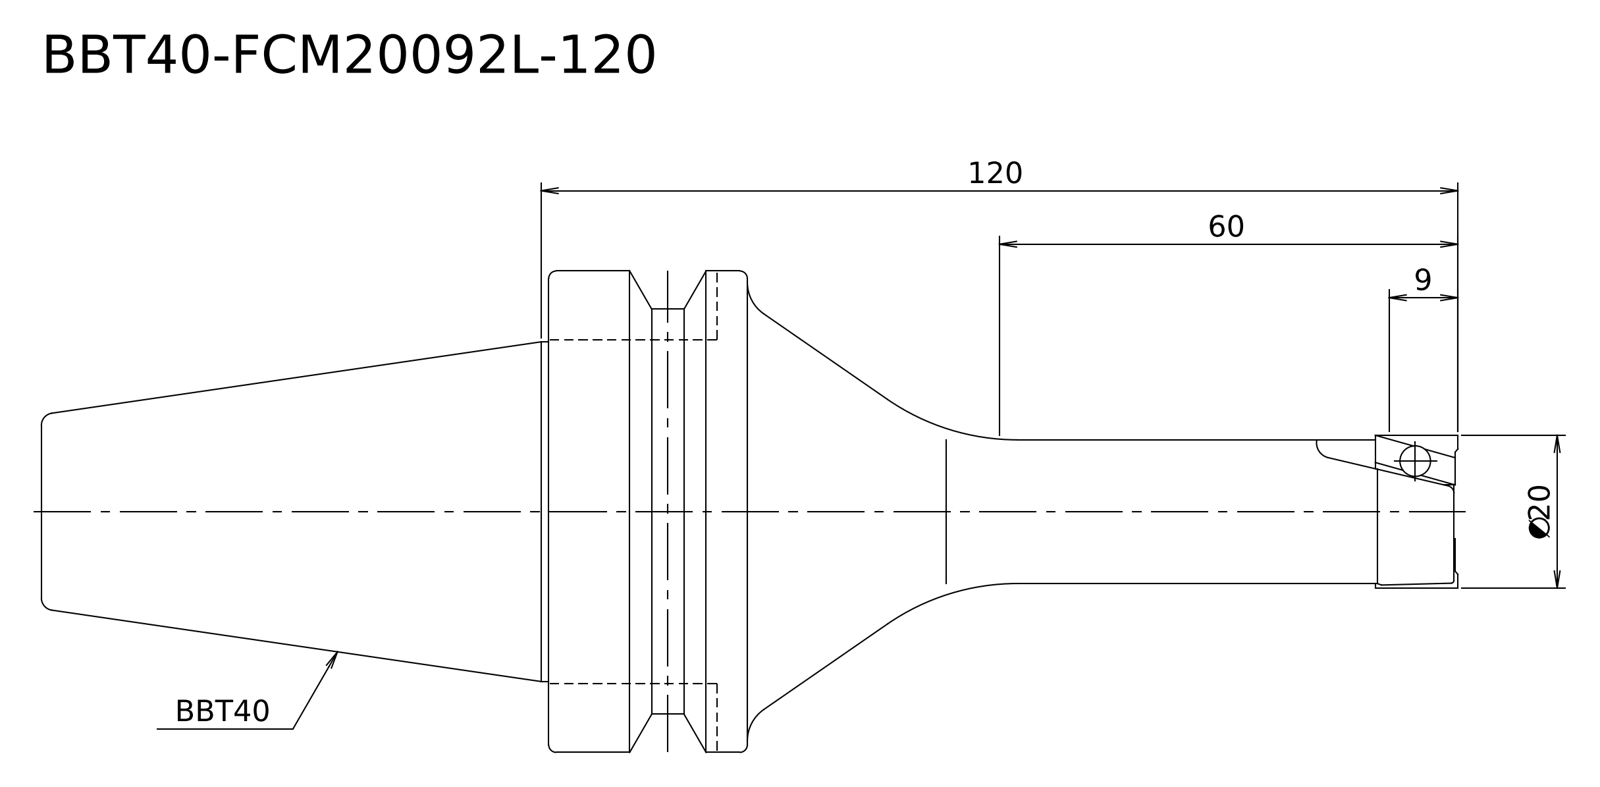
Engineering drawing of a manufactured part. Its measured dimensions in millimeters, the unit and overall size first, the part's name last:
Units: millimetres
Overall size (bounding box): 185.4 × 63 × 63
Round bosses / shafts (diameter × count): ⌀63 ×1, ⌀53 ×1, ⌀44.45 ×1, ⌀20 ×1, ⌀18.8 ×1
Main face-to-face distances: 66.4, 119, 185.4, 93, 26, 92.4
Volume: 191 230 mm³ · Surface area: 24 160 mm²
Bodies: 1 solid, 17 faces (4 planar, 6 cylindrical, 7 other)
STEP written by: Kubotek KeyCreator V8.5.1 (14335) (CONFIG_CONTROL_DESIGN)
